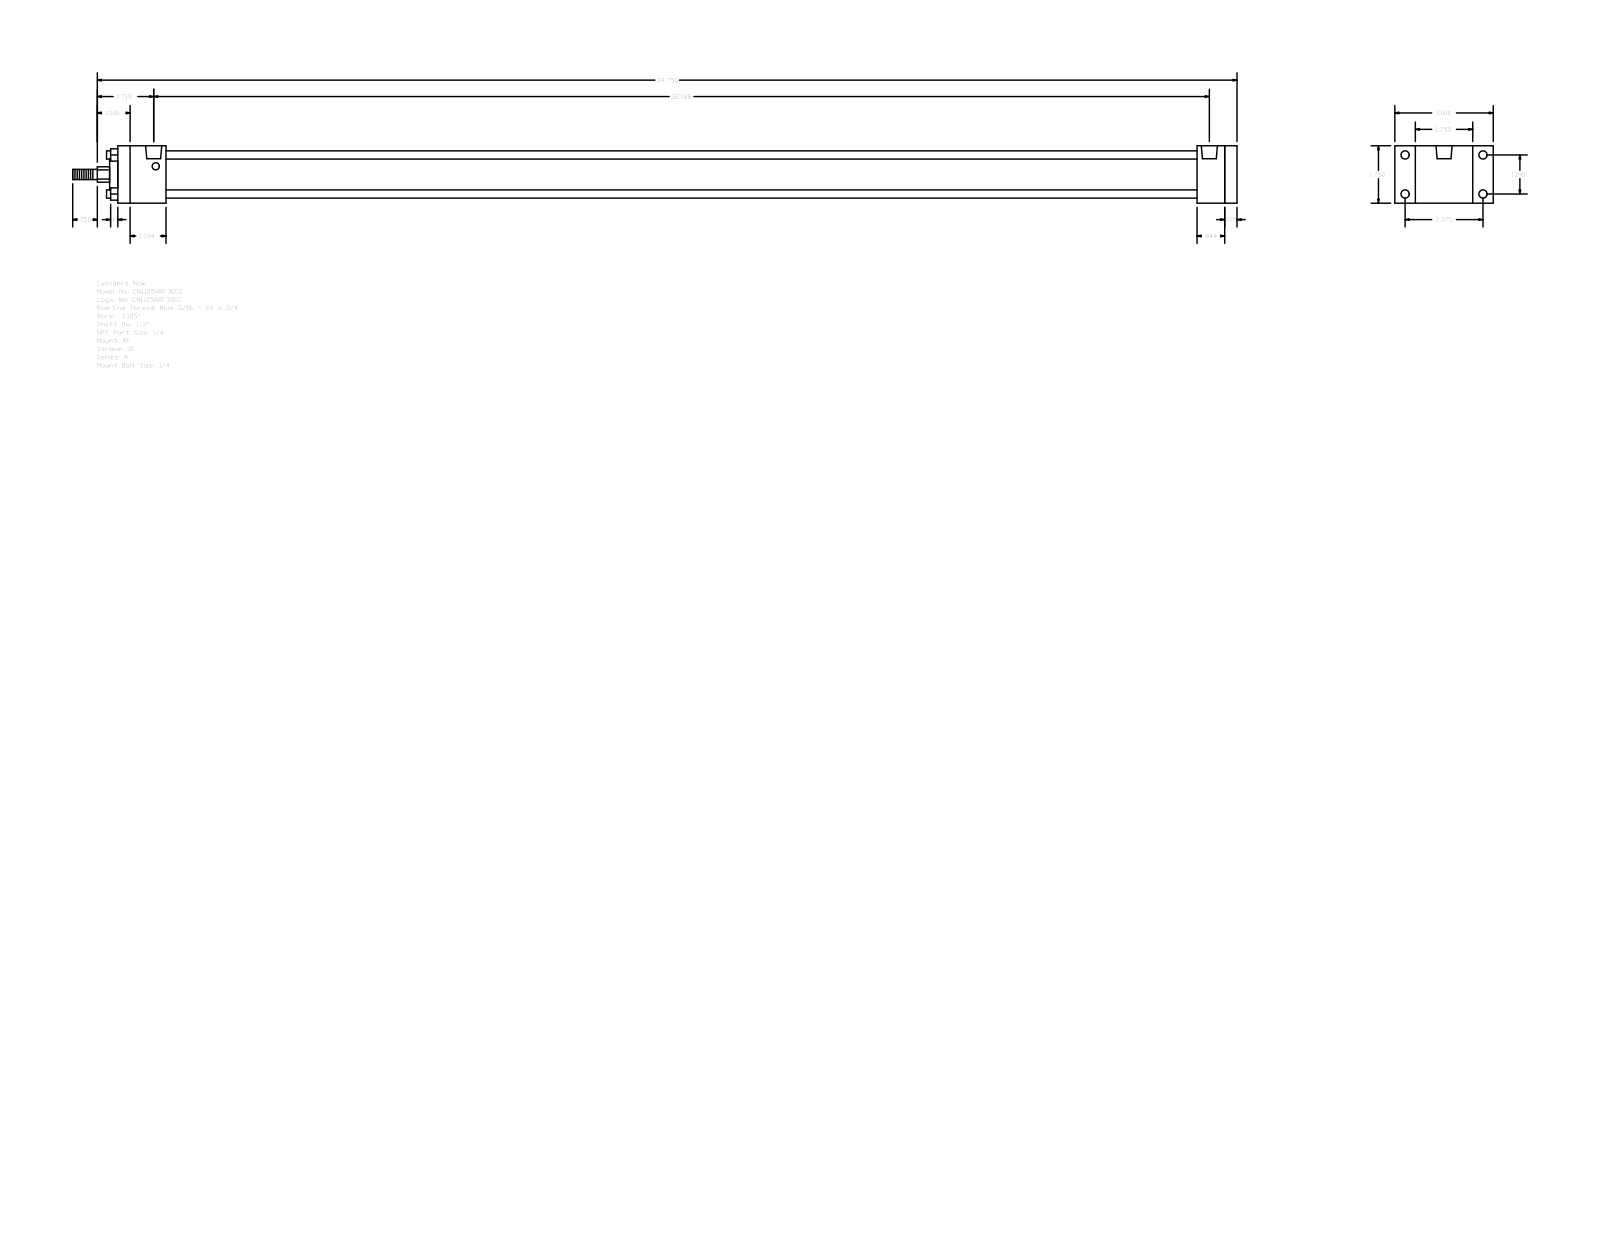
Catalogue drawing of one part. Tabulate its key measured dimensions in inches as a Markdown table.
| quantity | value |
| --- | --- |
| part name | A_RF__0112_0.5 |
| STEP written by | GSSL Pune (CONFIG_CONTROL_DESIGN) |
| units | inches |
| bodies | 0 solids, 92 faces (64 planar, 28 cylindrical, 0 other) |
| overall size | 35.5 × 3 × 1.75 |
| round holes (diameter × count) | 0.219 × 4, 0.25 × 4, 0.492 × 2 |
| round bosses / shafts (diameter × count) | 0.25 × 4, 1.255 × 1, 0.937 × 1, 0.5 × 1, 0.313 × 1 |
| partial cylindrical surfaces (radius × count) | 0.234 × 1 |
| main face-to-face distances | 1.75, 0.375, 34.125, 33.75, 1.469, 32.906, 31.437, 32.281, 32.656, 0.844 |
| hole center spacings | 1.19, 2.375, 2.656, 32.063, 0.062, 0.063, 32.125, 32.125 |
